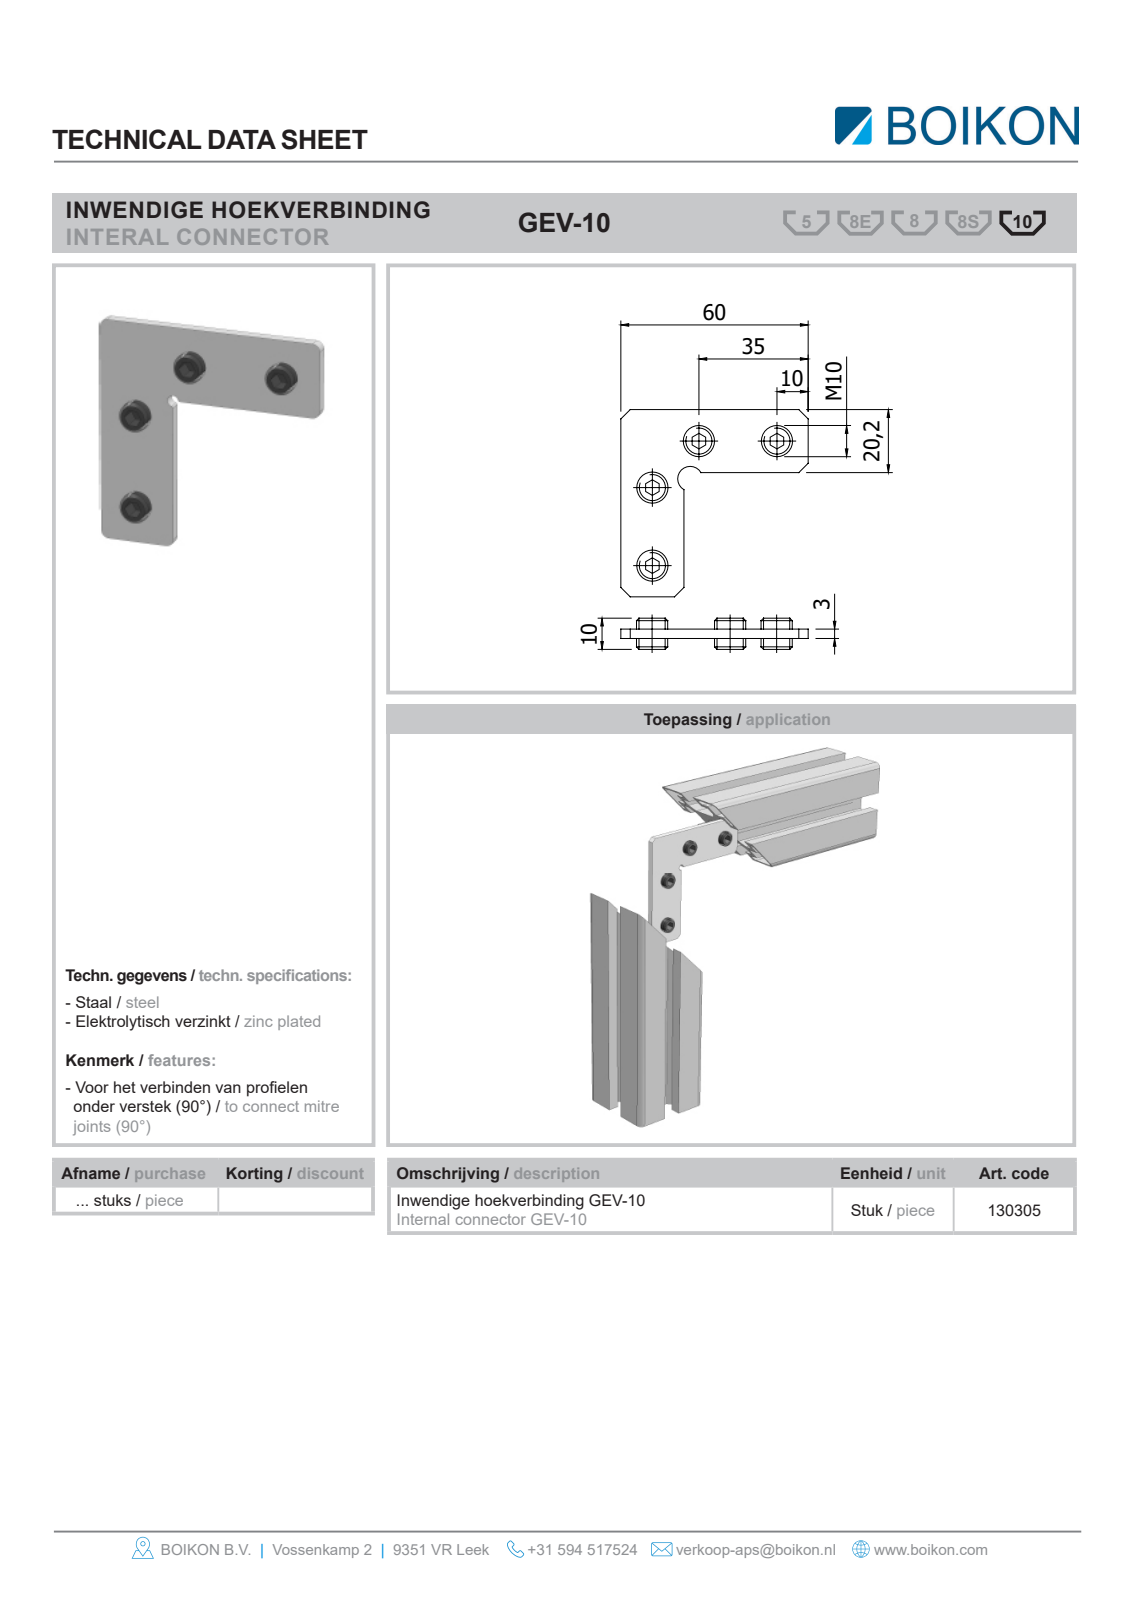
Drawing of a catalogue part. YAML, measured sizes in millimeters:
part_name: "Root; 130305Inwendige hoekverbinding GEV-10BOIKON; 901112Binnenzesk. DIN 916 EV M8 x 10BOIKON0"
step_written_by: "HiCAD 2013 1802.4 Build 509 (AUTOMOTIVE_DESIGN)"
units: millimeters
bodies: {solids: 5, faces: 56, planar: 40, cylindrical: 8, other: 8}
overall_size: [72.5, 72.5, 19.5]
volume: 6375
surface_area: 5946
round_holes:
  - {diameter: 8, count: 4}
round_bosses_or_shafts:
  - {diameter: 6.47, count: 4}
face_to_face_distances: [3, 20, 40, 4, 60, 6, 8, 12, 5, 2]
hole_center_spacings: [25, 42.72, 21.21, 56.57]
